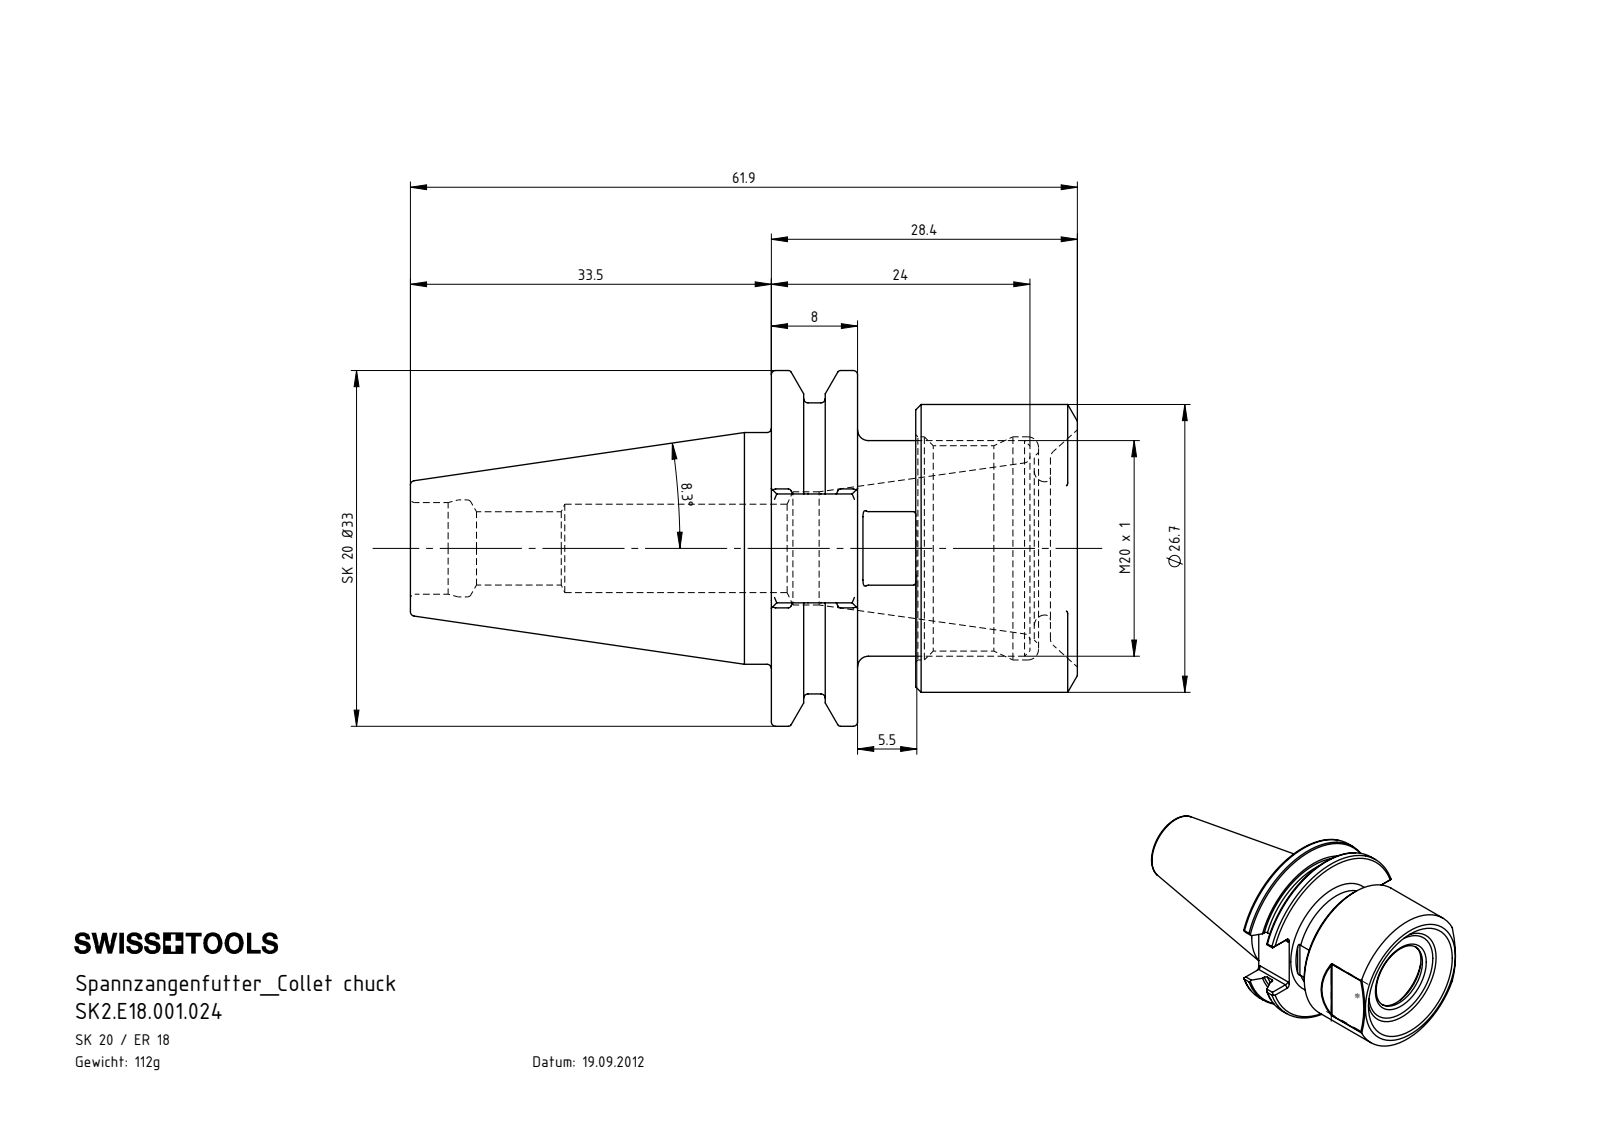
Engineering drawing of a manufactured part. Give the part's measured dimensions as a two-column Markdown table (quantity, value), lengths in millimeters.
| quantity | value |
| --- | --- |
| part name | SK2-E18.001.024; E18-ER1.001.015 |
| STEP written by | SolidWorks 2012 (CONFIG_CONTROL_DESIGN) |
| units | millimeters |
| bodies | 2 solids, 169 faces (45 planar, 50 cylindrical, 74 other) |
| overall size | 61.9 × 33 × 31.1 |
| volume | 17 548 mm³ |
| surface area | 9 599 mm² |
| round holes (diameter × count) | 6.8 × 1, 8.2 × 1, 8.5 × 1, 9 × 1, 10.5 × 1, 19.05 × 1, 20.7 × 1 |
| round bosses / shafts (diameter × count) | 26.7 × 1, 21.5 × 1, 20 × 1 |
| partial cylindrical surfaces (radius × count) | 0.5 × 12, 0.2 × 6, 0.3 × 4, 13.5 × 1, 16.5 × 1 |
| main face-to-face distances | 8, 23.4, 13.4, 5.4, 24, 0.6, 17.9, 25.9, 12.5, 0.4 |
